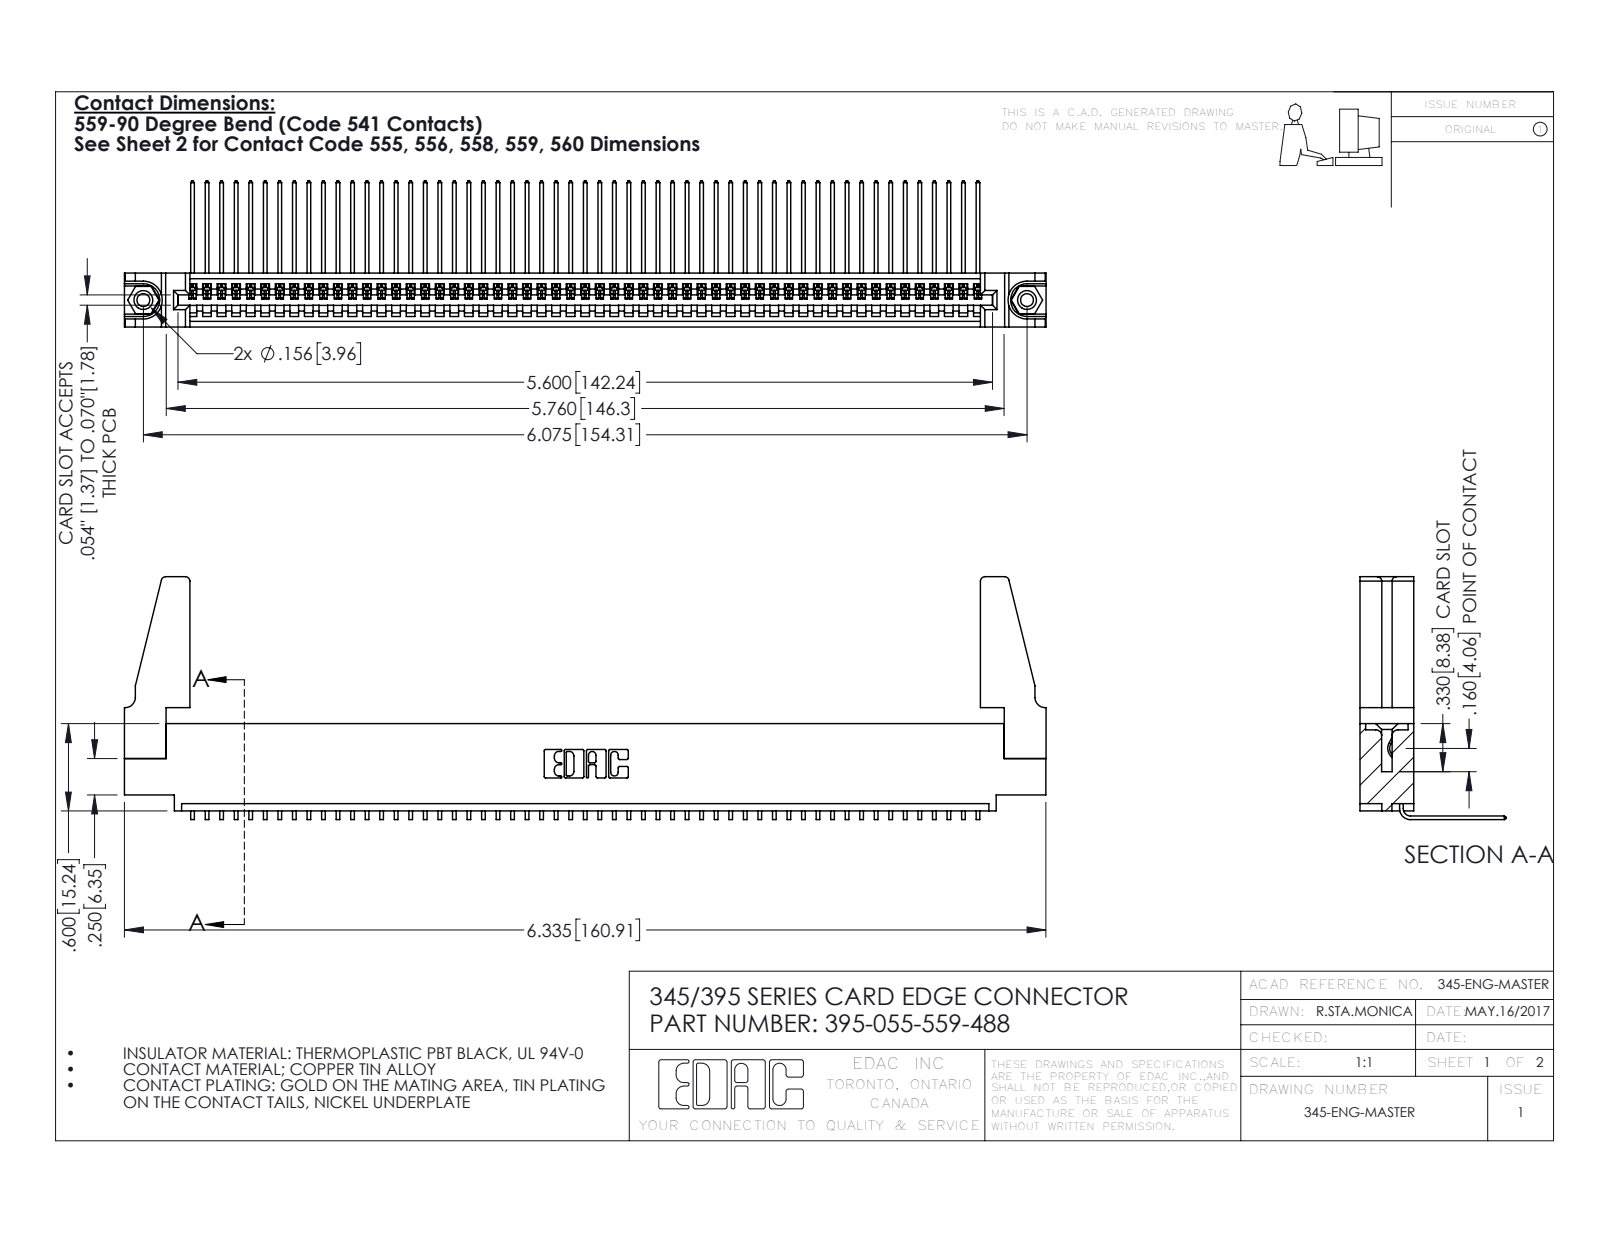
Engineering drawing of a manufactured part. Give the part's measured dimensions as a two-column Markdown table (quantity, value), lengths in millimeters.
| quantity | value |
| --- | --- |
| part name | 345-220-078_345-220-088; 345-292-001_558 559 Tail - 1; 395-055-559-488; 345-250-001_345-250-001-102 (+1 more) |
| STEP written by | SolidWorks 2016 (CONFIG_CONTROL_DESIGN) |
| units | millimeters |
| bodies | 60 solids, 3554 faces (2466 planar, 1072 cylindrical, 16 other) |
| overall size | 160.9 × 42.4 × 25.5 |
| volume | 18 750 mm³ |
| surface area | 25 060 mm² |
| round holes (diameter × count) | 2.3 × 2, 3.2 × 2, 4 × 2, 1.6 × 1 |
| round bosses / shafts (diameter × count) | 3.9 × 2 |
| partial cylindrical surfaces (radius × count) | 0.2 × 110, 0.3 × 22, 0.8 × 8, 0.2 × 6, 0.8 × 6, 0.7 × 3, 0.8 × 2, 1 × 2 |
| main face-to-face distances | 1.8, 7.6, 9.4, 5.1, 2.5, 6.9, 0.6, 5.7, 3.8, 1.8 |
| hole center spacings | 6.9, 148.3, 154.3 |
